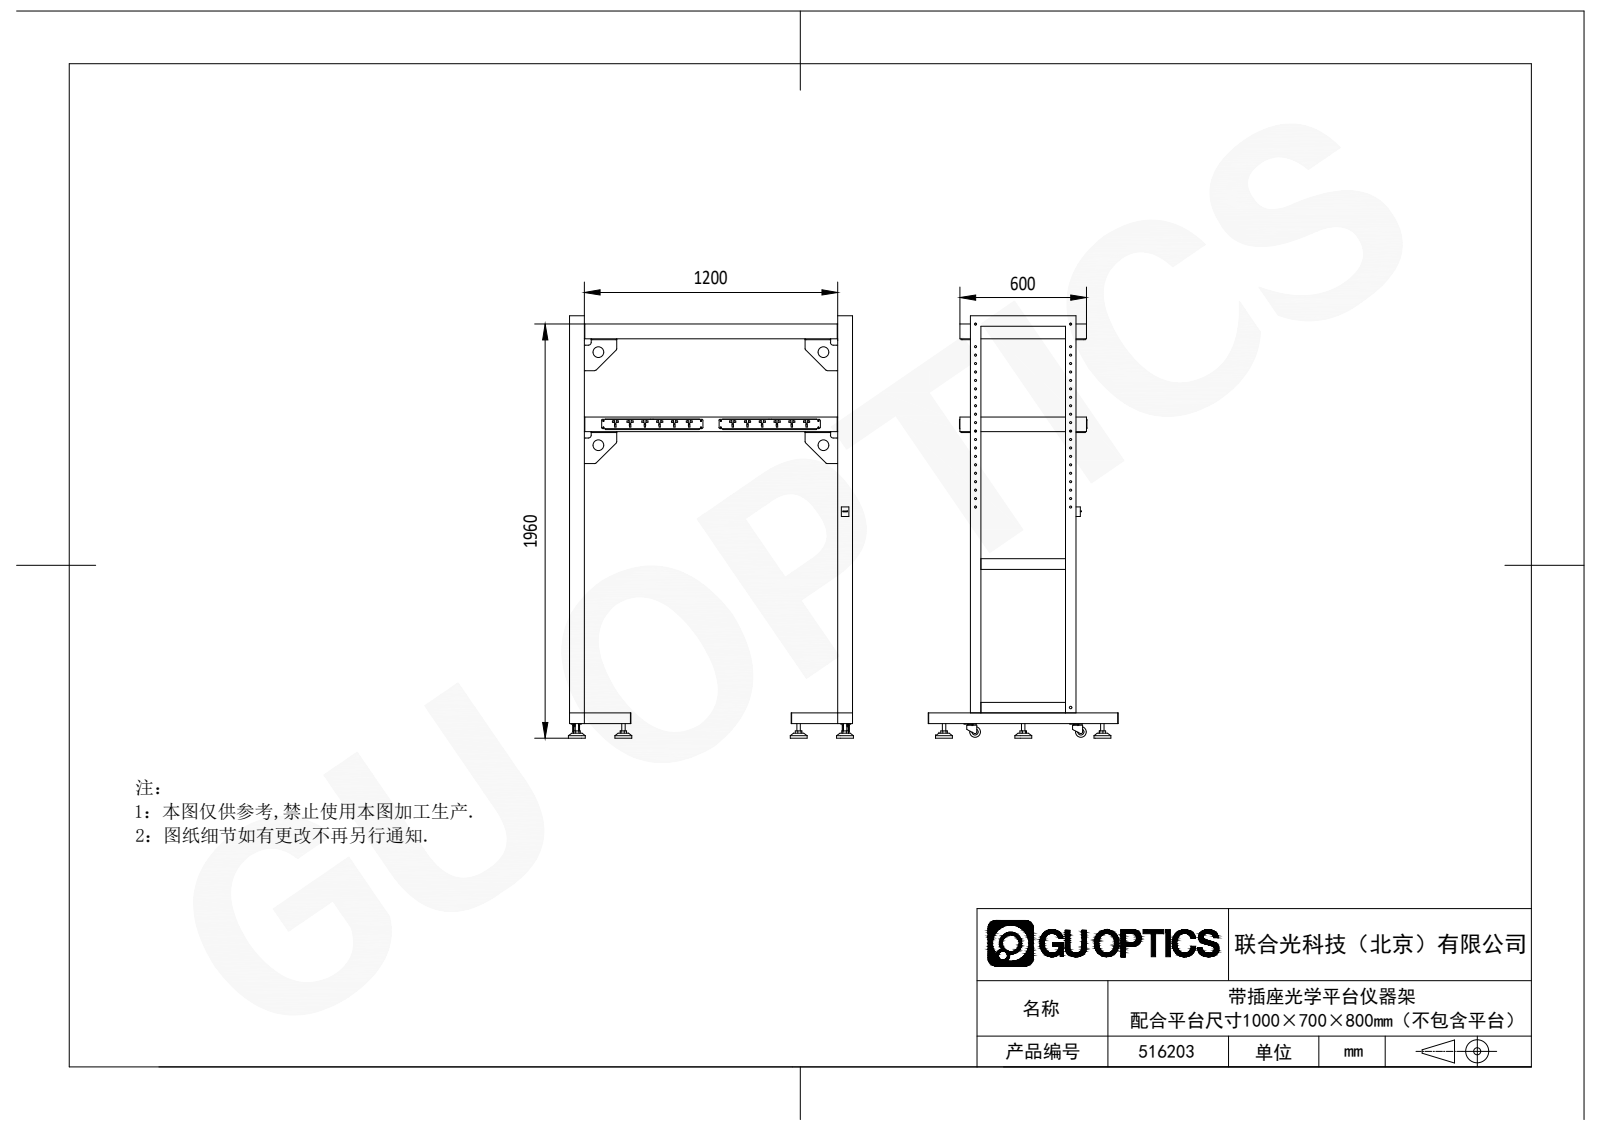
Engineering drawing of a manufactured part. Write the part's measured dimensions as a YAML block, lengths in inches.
part_name: "516203"
step_written_by: "SolidWorks 2020 (CONFIG_CONTROL_DESIGN)"
units: inches
bodies: {solids: 59, faces: 2581, planar: 1449, cylindrical: 1056, other: 76}
overall_size: [78.78, 53.15, 35.433]
volume: 1165
surface_area: 19440
round_holes:
  - {diameter: 0.354, count: 66}
  - {diameter: 0.24, count: 16}
  - {diameter: 0.394, count: 16}
  - {diameter: 0.256, count: 12}
  - {diameter: 0.165, count: 8}
  - {diameter: 0.205, count: 8}
  - {diameter: 0.236, count: 8}
  - {diameter: 0.669, count: 6}
  - {diameter: 0.709, count: 6}
  - {diameter: 1.024, count: 6}
  - {diameter: 2.717, count: 6}
  - {diameter: 0.126, count: 4}
round_bosses_or_shafts:
  - {diameter: 3.15, count: 6}
  - {diameter: 0.63, count: 6}
  - {diameter: 1.024, count: 4}
  - {diameter: 0.709, count: 4}
  - {diameter: 1.969, count: 2}
  - {diameter: 0.394, count: 2}
partial_cylinders:
  - {radius: 0.197, count: 36}
  - {radius: 0.276, count: 24}
  - {radius: 0.118, count: 16}
  - {radius: 0.167, count: 12}
  - {radius: 0.059, count: 8}
  - {radius: 0.059, count: 8}
  - {radius: 0.158, count: 8}
  - {radius: 0.512, count: 4}
face_to_face_distances: [0.079, 0.118, 17.323, 2.756, 1.969, 0.059, 17.717, 50, 2.638, 1.89]
hole_center_spacings: [1.575, 3.15, 4.724, 11.024, 6.299, 7.874, 9.449, 12.598]
